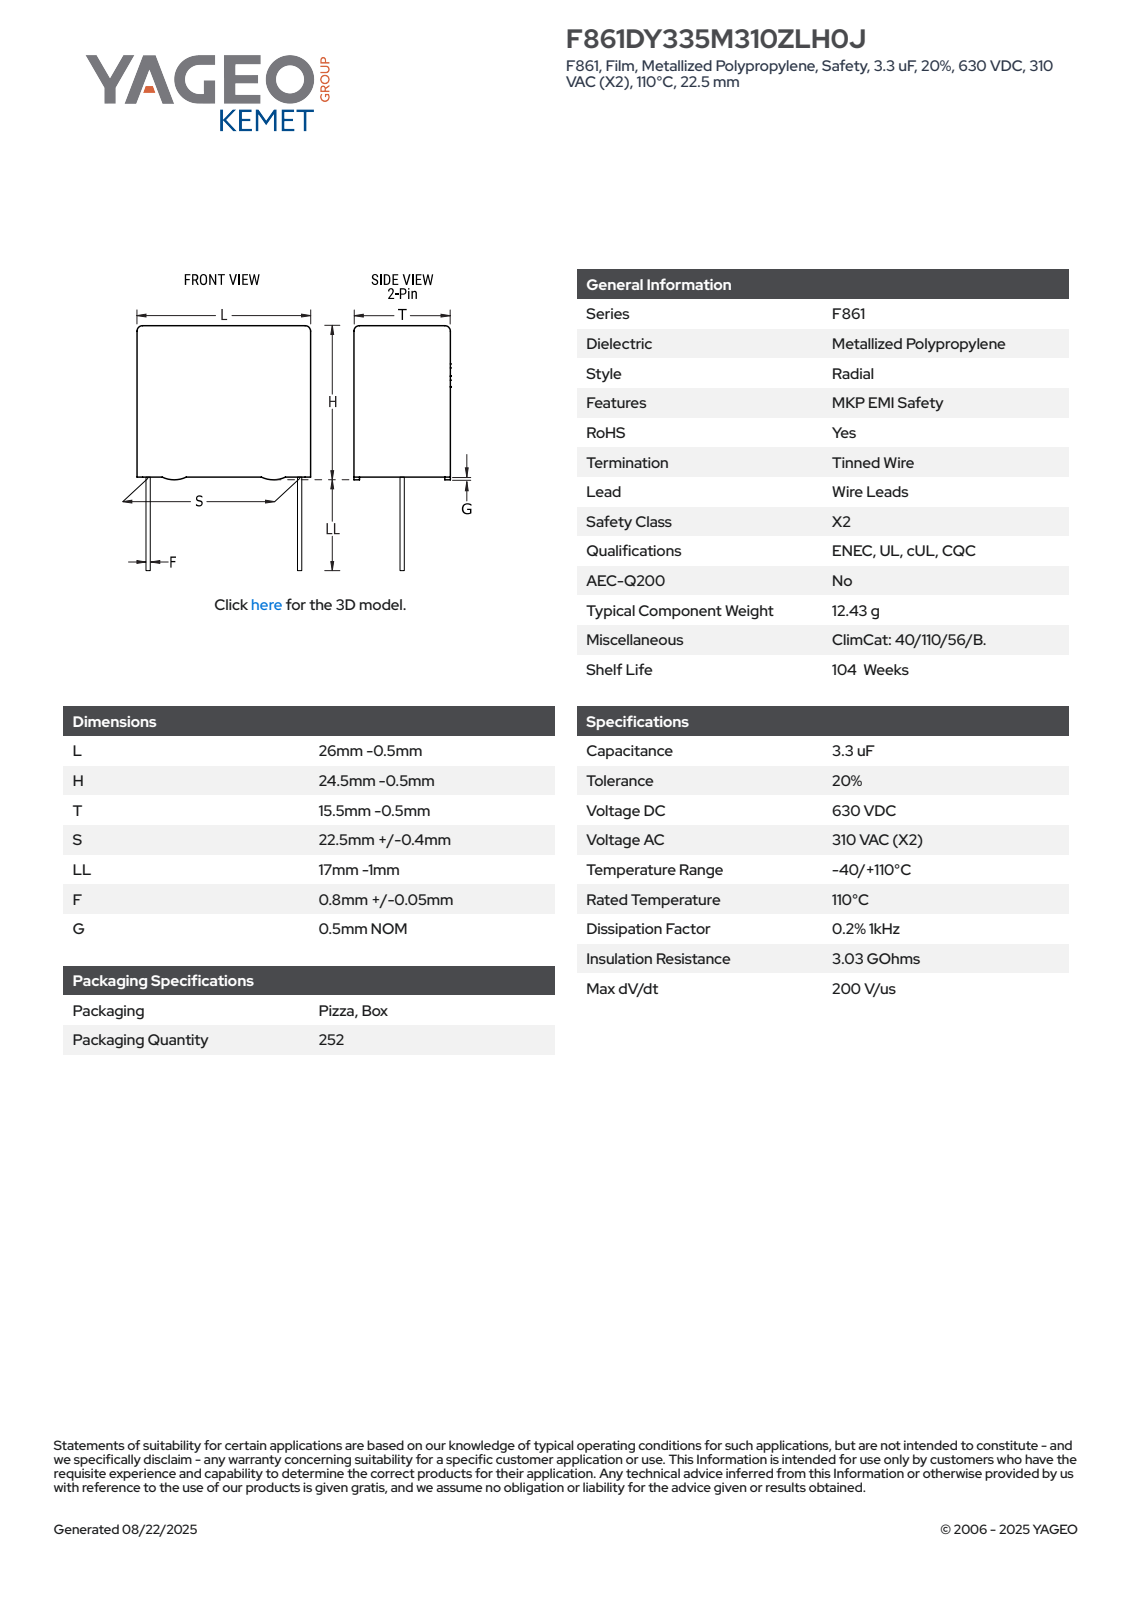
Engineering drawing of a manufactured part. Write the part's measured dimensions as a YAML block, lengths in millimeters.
part_name: "CFR_RBG_26X24.5X15.5_L25.5H24T15S22.5LL16F0.85G0.5"
step_written_by: "SolidWorks 2014 (AUTOMOTIVE_DESIGN)"
units: millimeters
bodies: {solids: 4, faces: 89, planar: 81, cylindrical: 8, other: 0}
overall_size: [40, 25.5, 15.01]
volume: 9010
surface_area: 2828
round_bosses_or_shafts:
  - {diameter: 0.85, count: 2}
partial_cylinders:
  - {radius: 0.5, count: 4}
face_to_face_distances: [15, 25.5, 23.5, 0.5, 24, 0.85, 14.14, 0.86, 13.29, 14.15]
